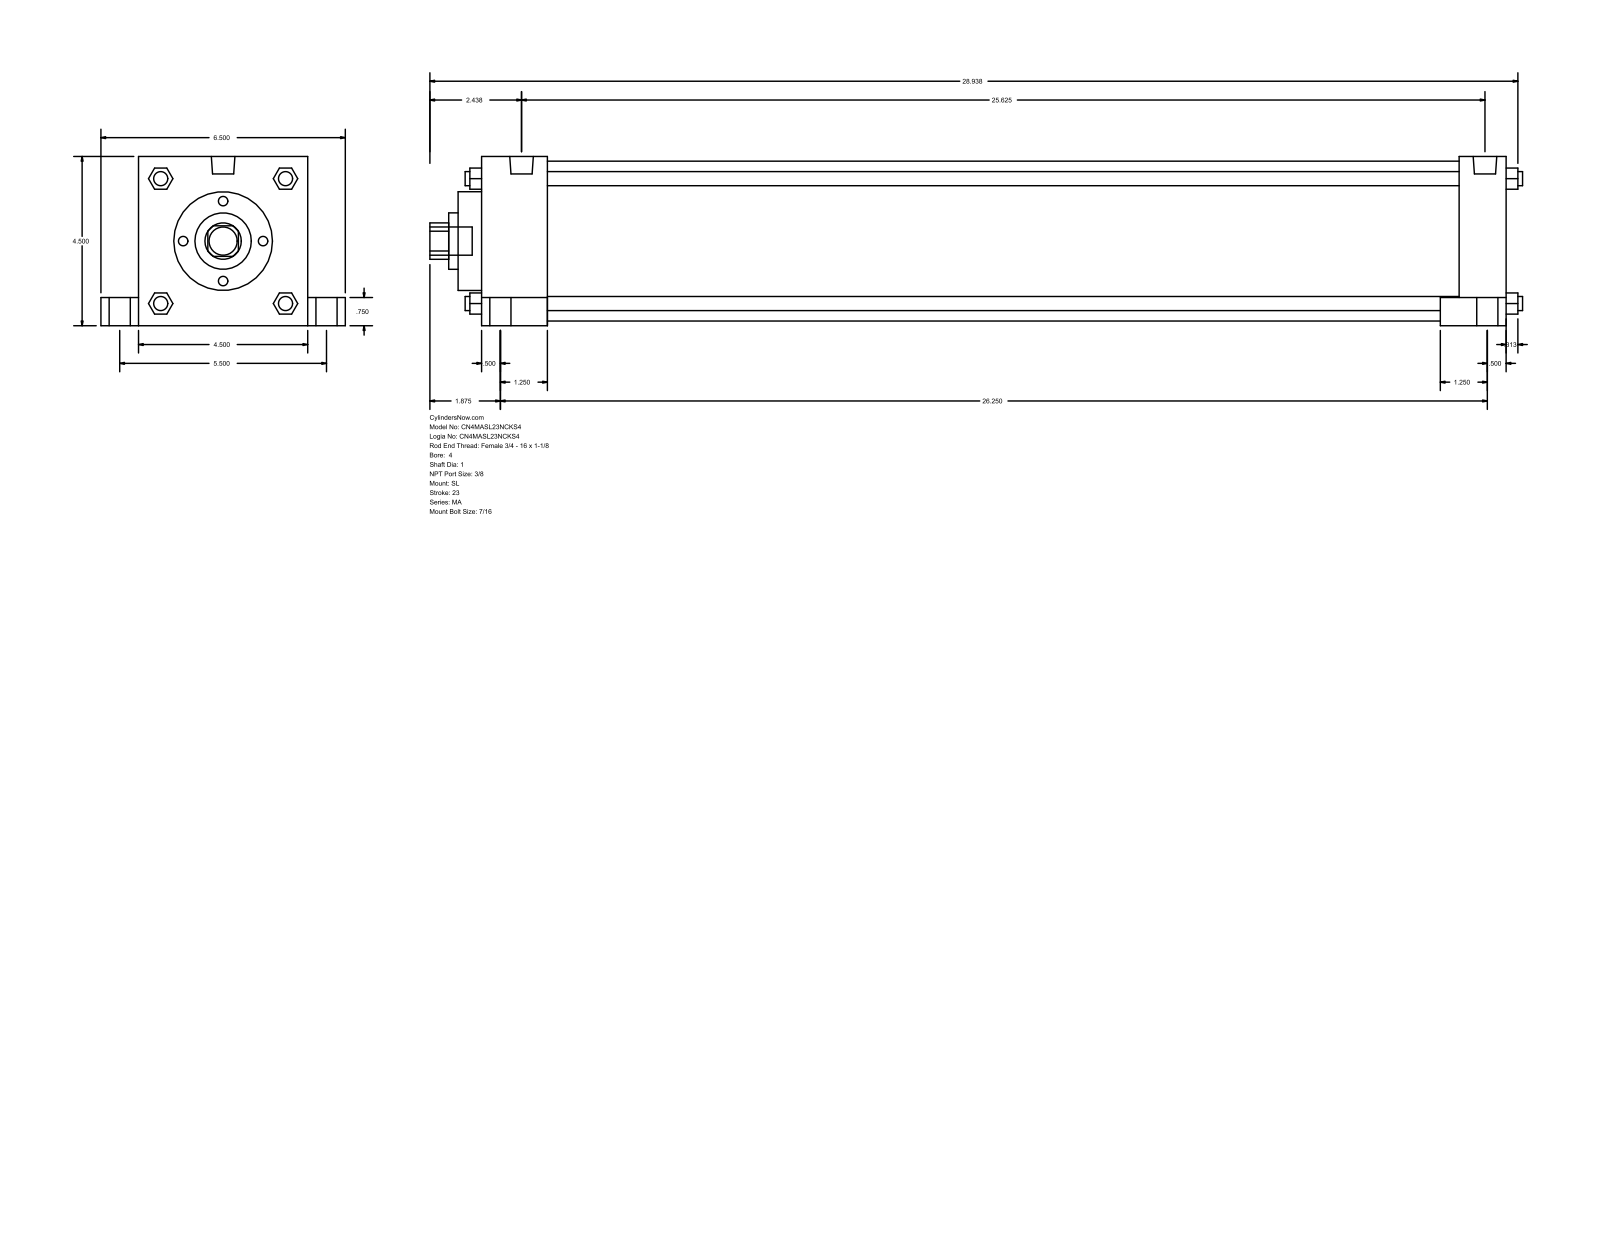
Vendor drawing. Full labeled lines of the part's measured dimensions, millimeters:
Part name (STEP PRODUCT): MA_SL__0400_1
STEP written by: GSSL Pune (CONFIG_CONTROL_DESIGN)
Units: millimetres
Bodies: 0 solids, 150 faces (113 planar, 37 cylindrical, 0 other)
Overall size (bounding box): 738.19 × 165.1 × 114.3
Round holes (diameter × count): ⌀25.4 ×1, ⌀38.1 ×1, ⌀66.67 ×1, ⌀107.95 ×1
Round bosses / shafts (diameter × count): ⌀20.64 ×4, ⌀14.29 ×4, ⌀11.11 ×4, ⌀9.53 ×4, ⌀15.93 ×2, ⌀19.05 ×1
Partial cylindrical surfaces — rounded edges, fillets, slot ends (radius × count): R12.29 ×1
Main face-to-face distances: 114.3, 692.16, 615.95, 44.46, 647.7, 660.41, 31.75, 25.4, 139.7, 19.05
